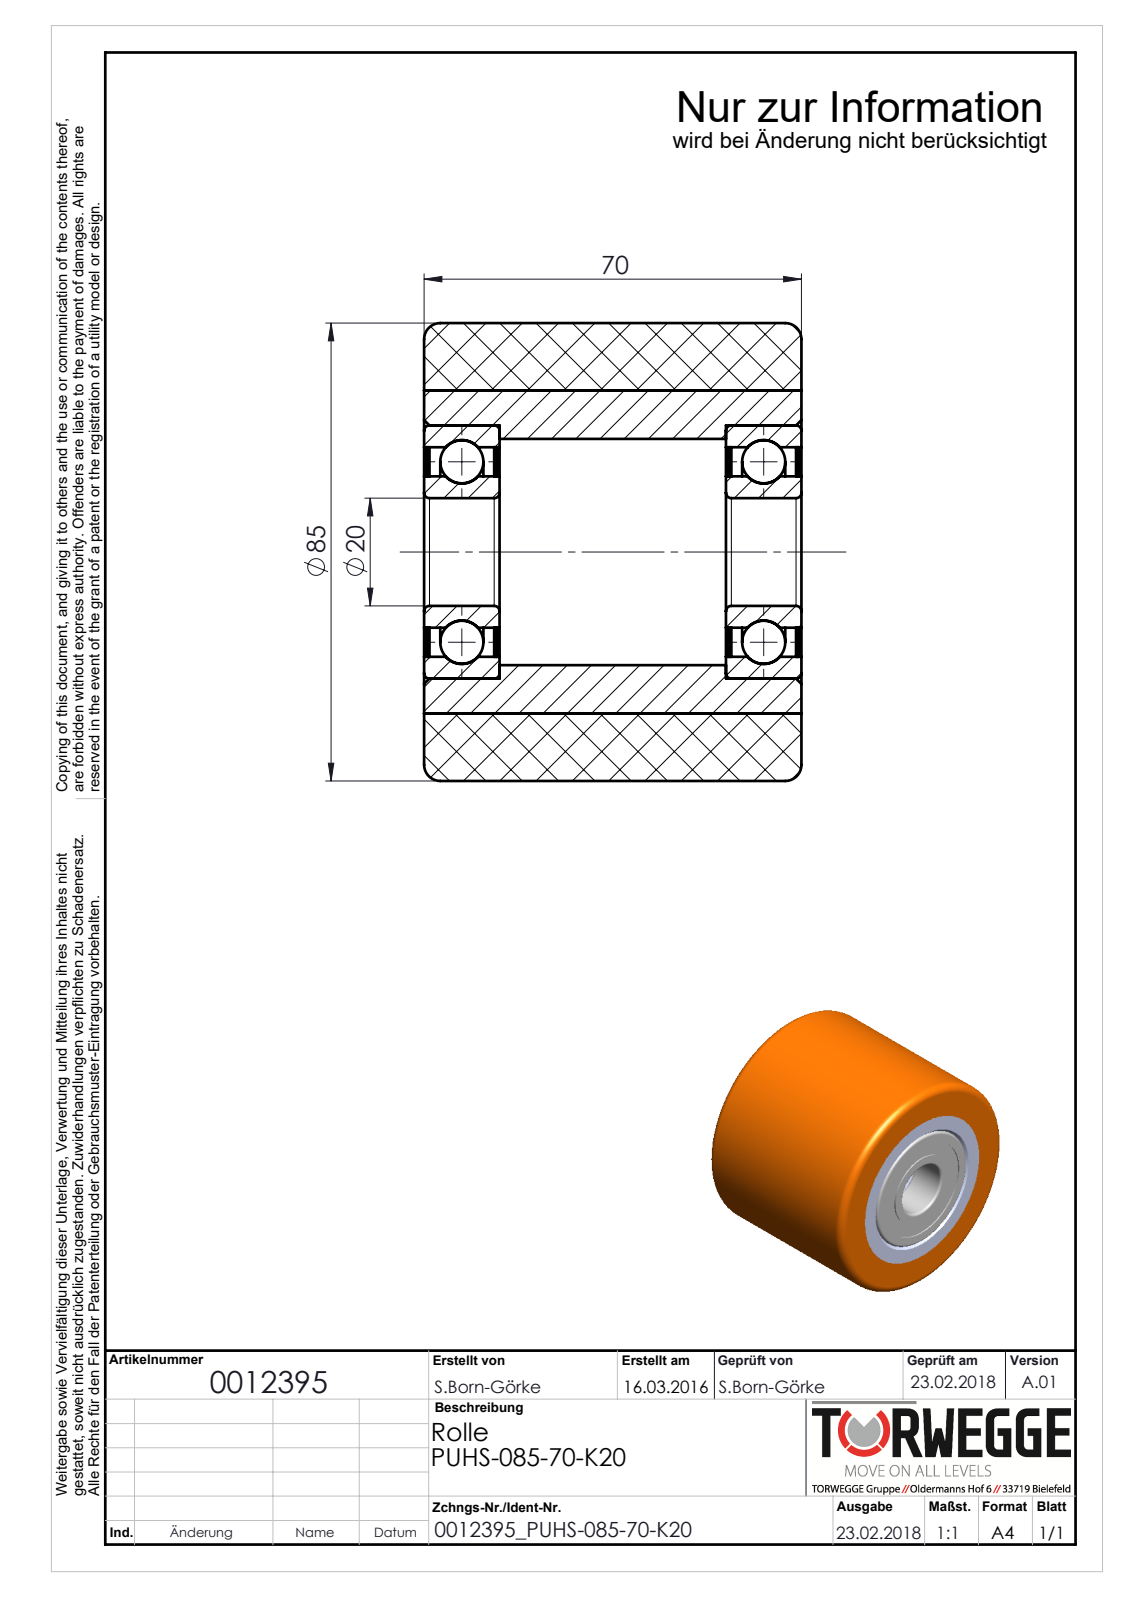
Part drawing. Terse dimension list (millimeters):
name: 0012395_PUHS-085-70-K20
written by: SolidWorks 2016 (AUTOMOTIVE_DESIGN)
unit: mm
bodies: 12 solids, 118 faces (22 planar, 52 cylindrical, 44 other)
size: 85 × 85 × 70
volume: 322 167 mm³; area: 87 906 mm²
holes: 1× ⌀20, 1× ⌀28.1, 1× ⌀38.9, 1× ⌀42, 1× ⌀47, 1× ⌀60
bosses: 1× ⌀85
face distances: 0.5, 56, 70, 13, 1, 13.5, 56.5, 12.5, 55.5, 14
